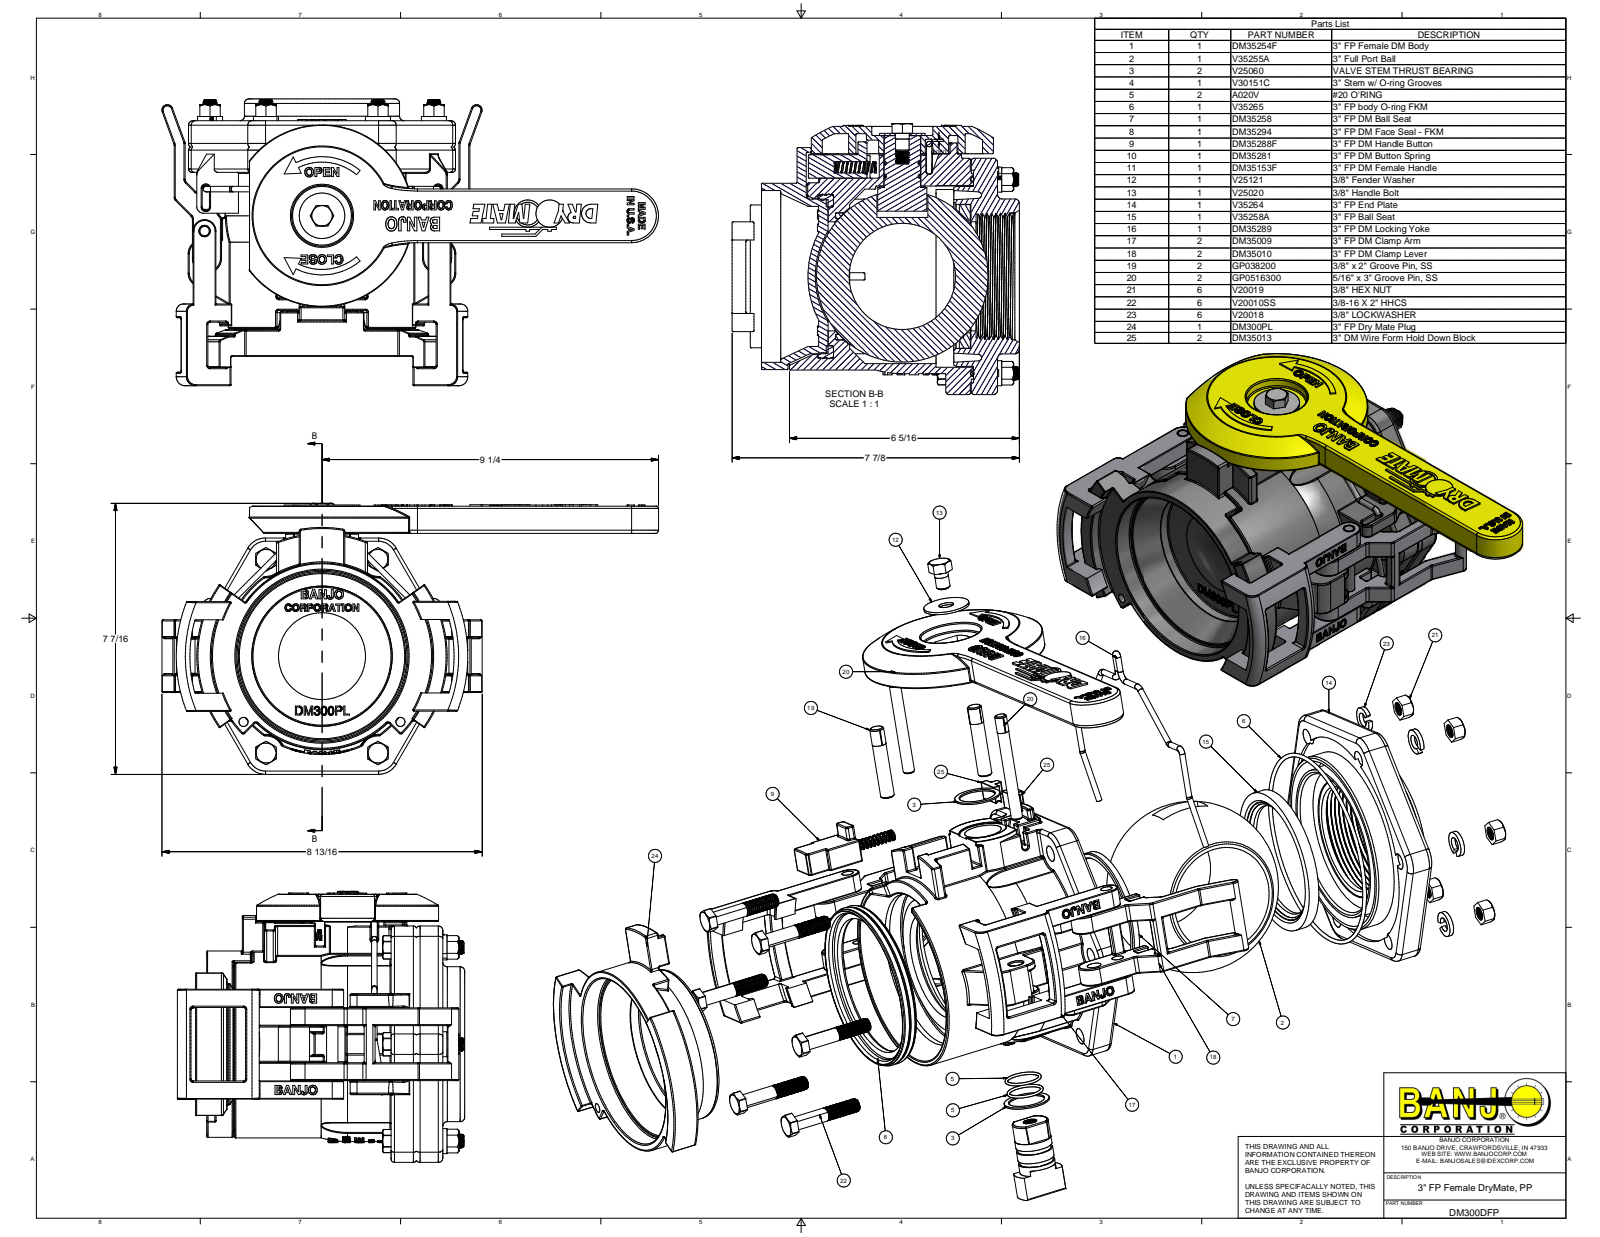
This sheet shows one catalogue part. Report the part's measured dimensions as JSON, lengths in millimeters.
{"part_name": "DM300DFP; DM35254F; DM35254FX; V35255A (+8 more)", "step_written_by": "Autodesk Inventor 2012 (AUTOMOTIVE_DESIGN)", "units": "millimeters", "bodies": {"solids": 45, "faces": 6044, "planar": 1771, "cylindrical": 1647, "other": 2626}, "overall_size": [346.4, 201.2, 189.3], "volume_mm3": 2214000, "surface_area_mm2": 607500, "round_holes": [[7.8, 6], [9.8, 6], [11.2, 6], [6.4, 2], [8, 2], [8.1, 2], [9.5, 2], [9.7, 2], [7.8, 1], [8, 1], [10.3, 1], [25.4, 1]], "round_bosses_or_shafts": [[8.2, 90], [3.8, 10], [9.5, 9], [17.4, 6], [9.8, 2], [8.3, 2], [7.9, 2], [7.6, 2]], "partial_cylinders_radius": [[0.8, 444], [1.5, 82], [0.5, 50], [3.2, 33], [2.3, 17], [4.1, 12], [0.3, 11], [0.8, 6]], "face_to_face_distances": [12.7, 19.1, 99.9, 51.1, 119, 60.3, 25.4, 51.3, 128.5, 12.4], "hole_center_spacings": [78.1, 78.1, 135.3, 51.5, 135.3, 156.2, 19.1, 26.8]}
